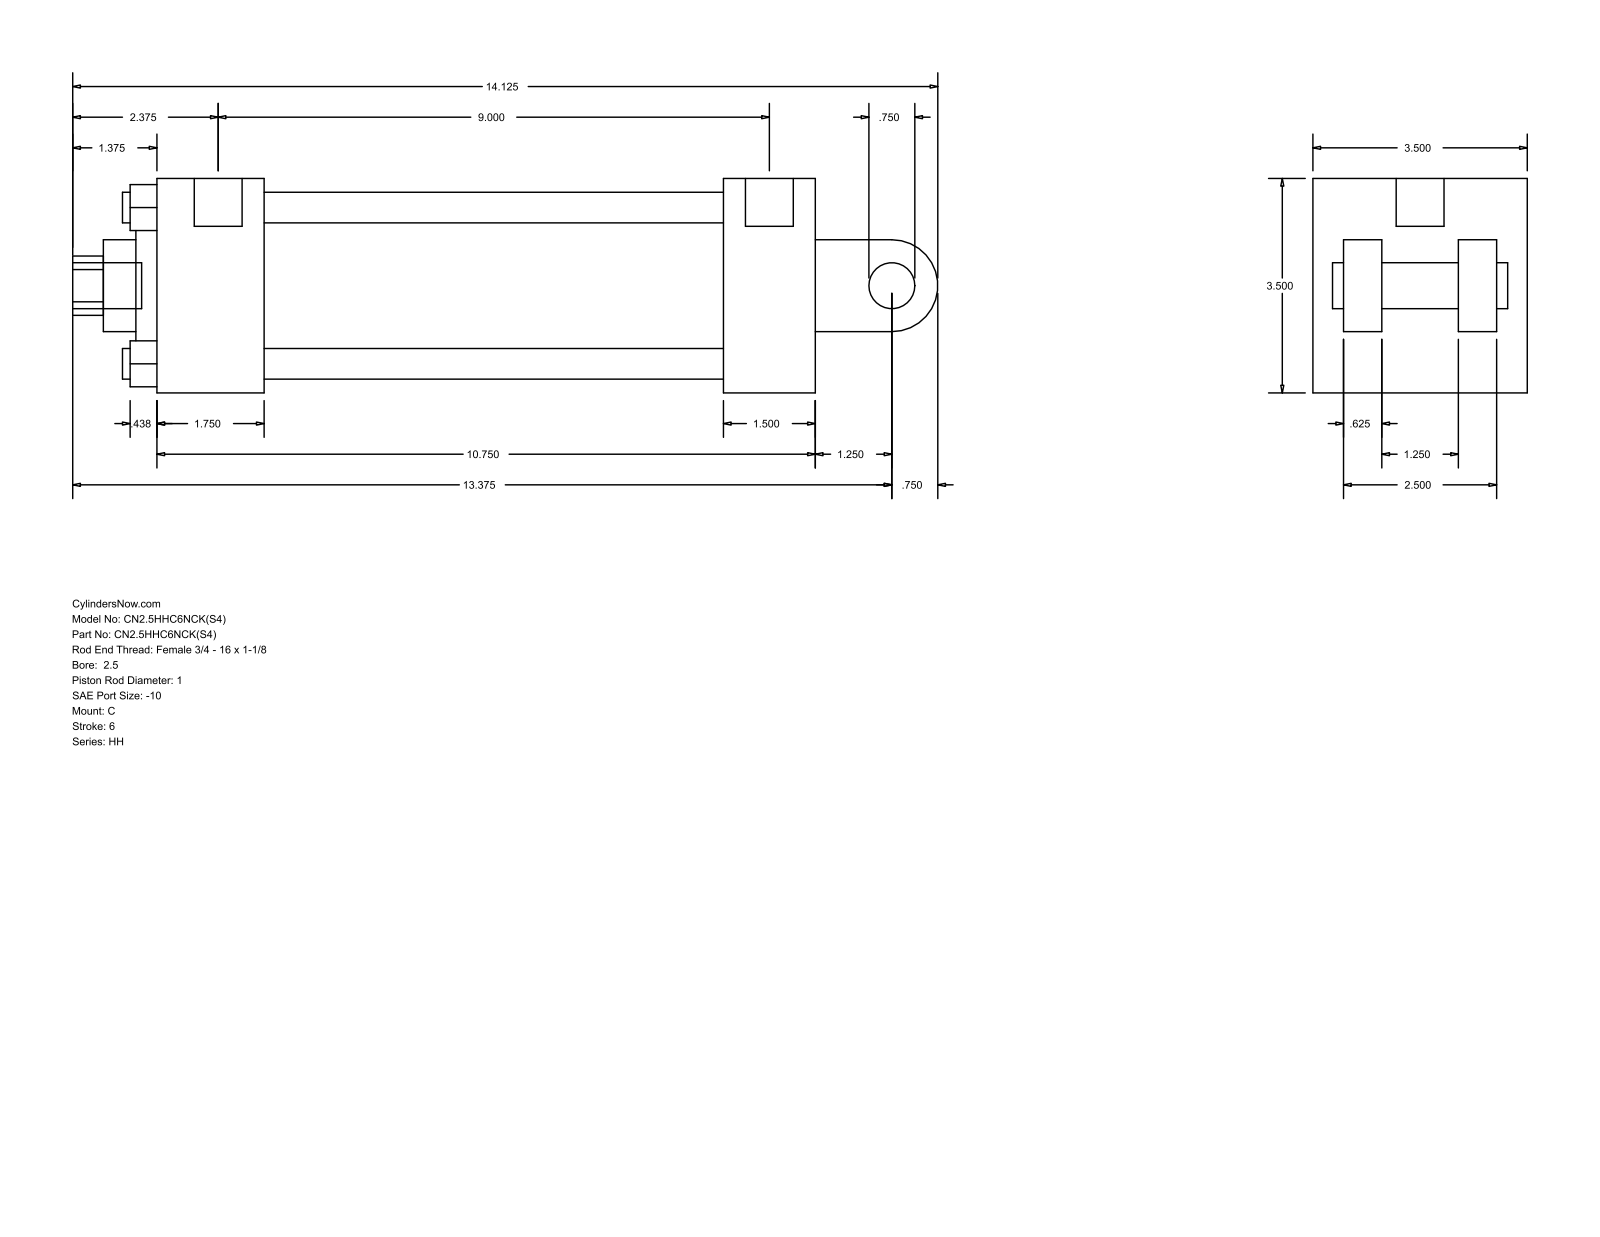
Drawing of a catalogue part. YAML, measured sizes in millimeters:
part_name: "HH_C__0250_1"
step_written_by: "GSSL Pune (CONFIG_CONTROL_DESIGN)"
units: millimeters
bodies: {solids: 0, faces: 101, planar: 71, cylindrical: 30, other: 0}
overall_size: [358.77, 88.9, 88.9]
round_holes:
  - {diameter: 12.7, count: 4}
  - {diameter: 5.56, count: 2}
  - {diameter: 19.84, count: 1}
  - {diameter: 25.4, count: 1}
  - {diameter: 38.1, count: 1}
  - {diameter: 60.33, count: 1}
  - {diameter: 73.03, count: 1}
round_bosses_or_shafts:
  - {diameter: 19.05, count: 2}
  - {diameter: 5.56, count: 2}
  - {diameter: 19.84, count: 1}
partial_cylinders:
  - {radius: 12.29, count: 1}
  - {radius: 19.05, count: 1}
face_to_face_distances: [88.9, 38.1, 273.06, 63.5, 15.87, 234.96, 44.46, 190.5, 228.6, 12.7]
hole_center_spacings: [45.79, 64.76, 91.58, 1.58]
